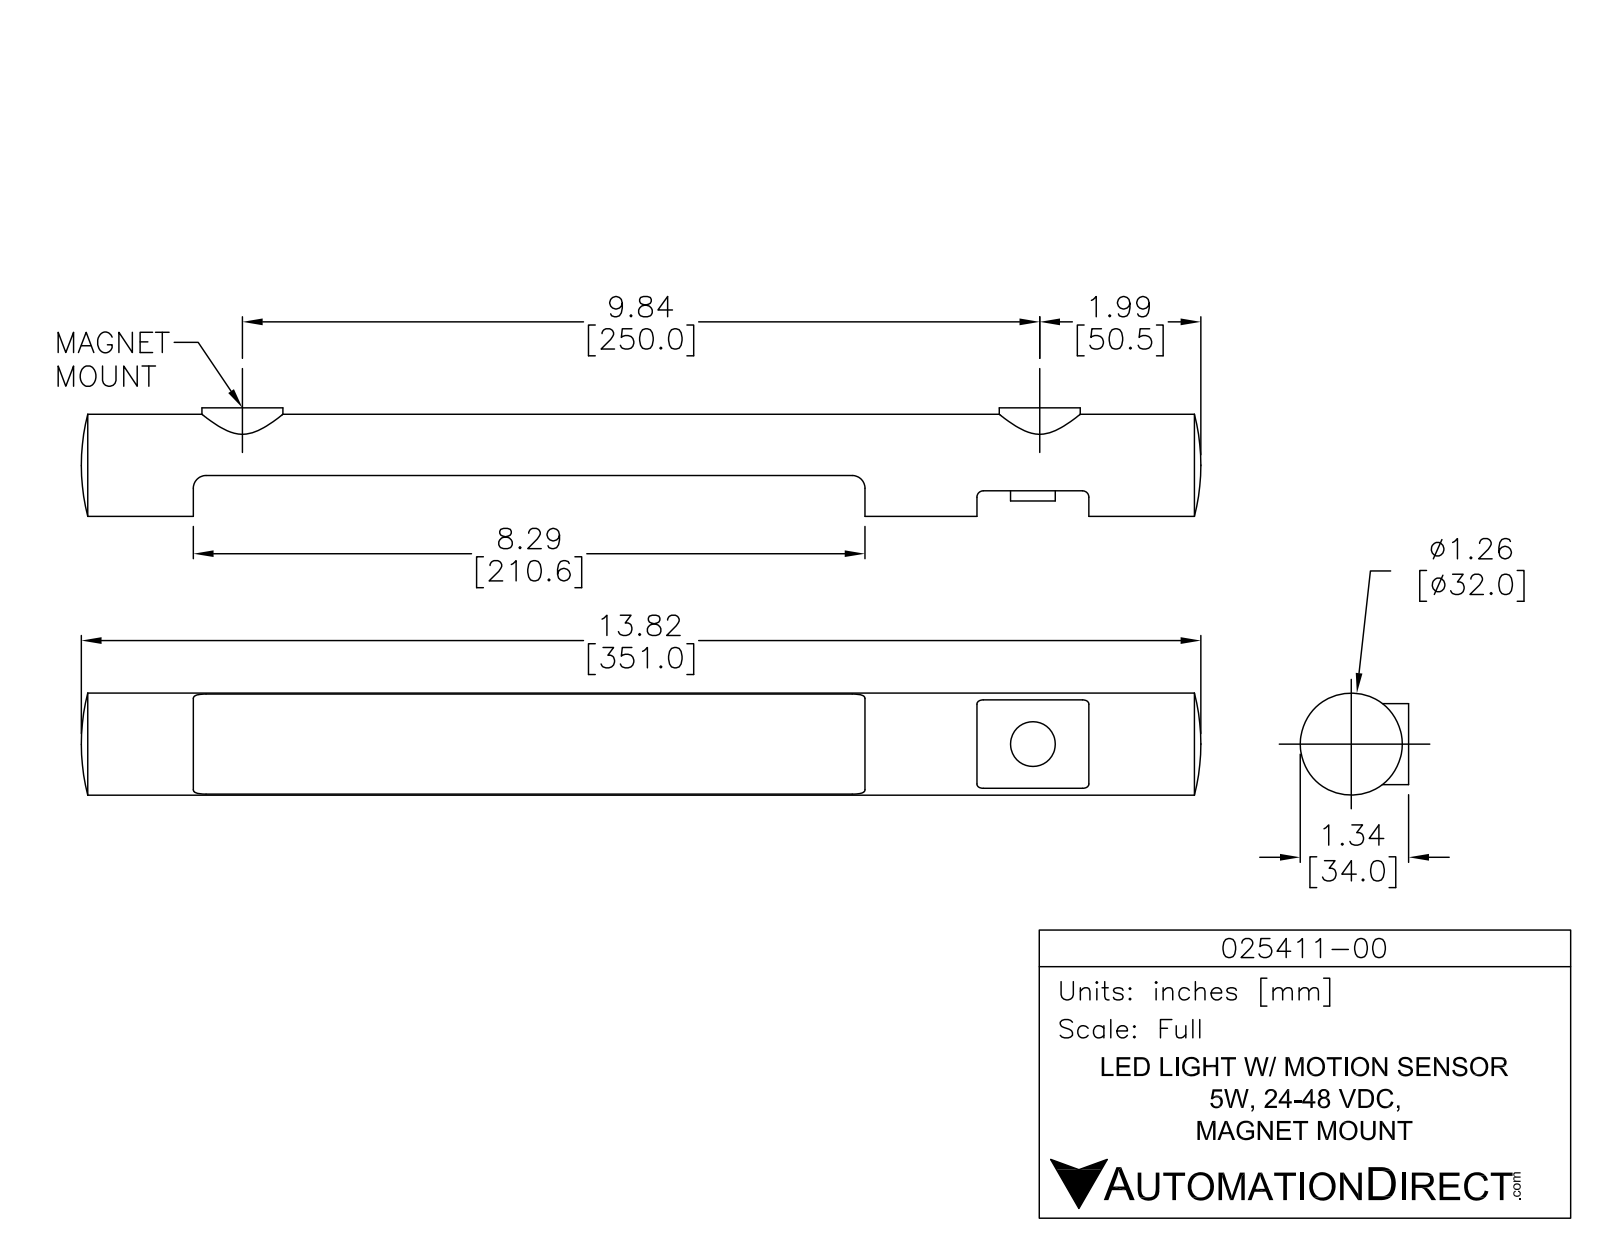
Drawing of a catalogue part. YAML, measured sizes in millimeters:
part_name: "025411-00"
step_written_by: "SolidWorks 2013 (AUTOMOTIVE_DESIGN)"
units: millimeters
bodies: {solids: 1, faces: 129, planar: 76, cylindrical: 33, other: 20}
overall_size: [349.5, 38.5, 32]
volume: 220600
surface_area: 37540
round_holes:
  - {diameter: 2, count: 2}
  - {diameter: 22.7, count: 1}
round_bosses_or_shafts:
  - {diameter: 25, count: 2}
  - {diameter: 1.9, count: 2}
  - {diameter: 32, count: 1}
  - {diameter: 22, count: 1}
  - {diameter: 22, count: 1}
partial_cylinders:
  - {radius: 1.5, count: 4}
  - {radius: 3, count: 2}
  - {radius: 5.1, count: 2}
  - {radius: 10.2, count: 2}
face_to_face_distances: [22.5, 0.8, 8.3, 1, 21.5, 13.5, 0.8, 13.8, 12.4, 9]
hole_center_spacings: [5.1]
